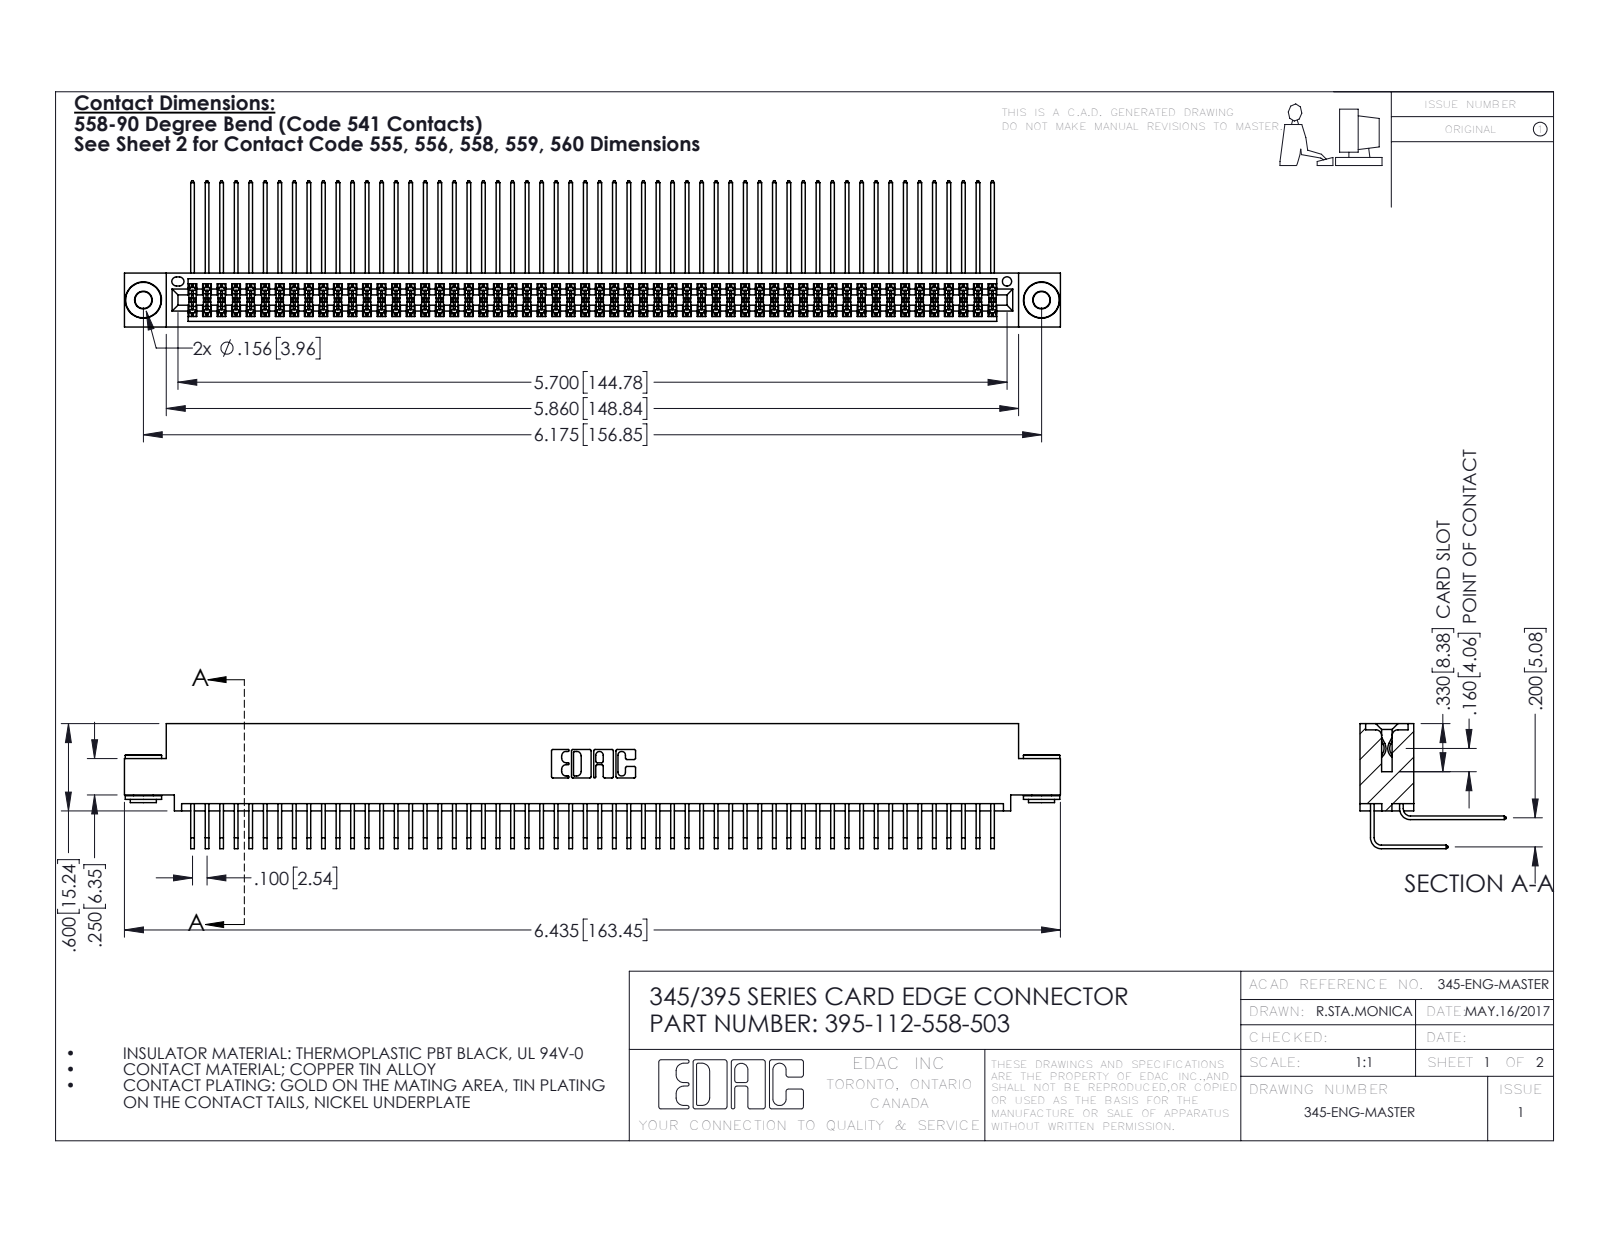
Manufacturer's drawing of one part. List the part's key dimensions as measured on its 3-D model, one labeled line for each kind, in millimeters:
Part name (STEP PRODUCT): 345-250-002_345-250-002-102; 345-292-001_558 559 Tail - 1; 345-292-001_558 Tail - 2; 395-112-558-503 (+1 more)
STEP written by: SolidWorks 2016 (CONFIG_CONTROL_DESIGN)
Units: millimetres
Bodies: 115 solids, 5992 faces (4014 planar, 1970 cylindrical, 8 other)
Overall size (bounding box): 163.4 × 25.5 × 21.8
Volume: 16 600 mm³ · Surface area: 28 140 mm²
Round holes (diameter × count): ⌀2.9 ×2, ⌀4 ×2, ⌀1.6 ×1
Round bosses / shafts (diameter × count): ⌀6.4 ×2, ⌀4.6 ×2, ⌀3.5 ×2
Partial cylindrical surfaces — rounded edges, fillets, slot ends (radius × count): R0.2 ×169, R0.3 ×22, R0.2 ×6, R0.8 ×6, R0.7 ×3, R0.4 ×2, R0.5 ×2, R0.6 ×2
Main face-to-face distances: 1.8, 7.6, 5.1, 0.6, 9.4, 2.5, 6.9, 5.7, 0.6, 4.4
Hole centre spacings: 6.9, 150.9, 156.8
